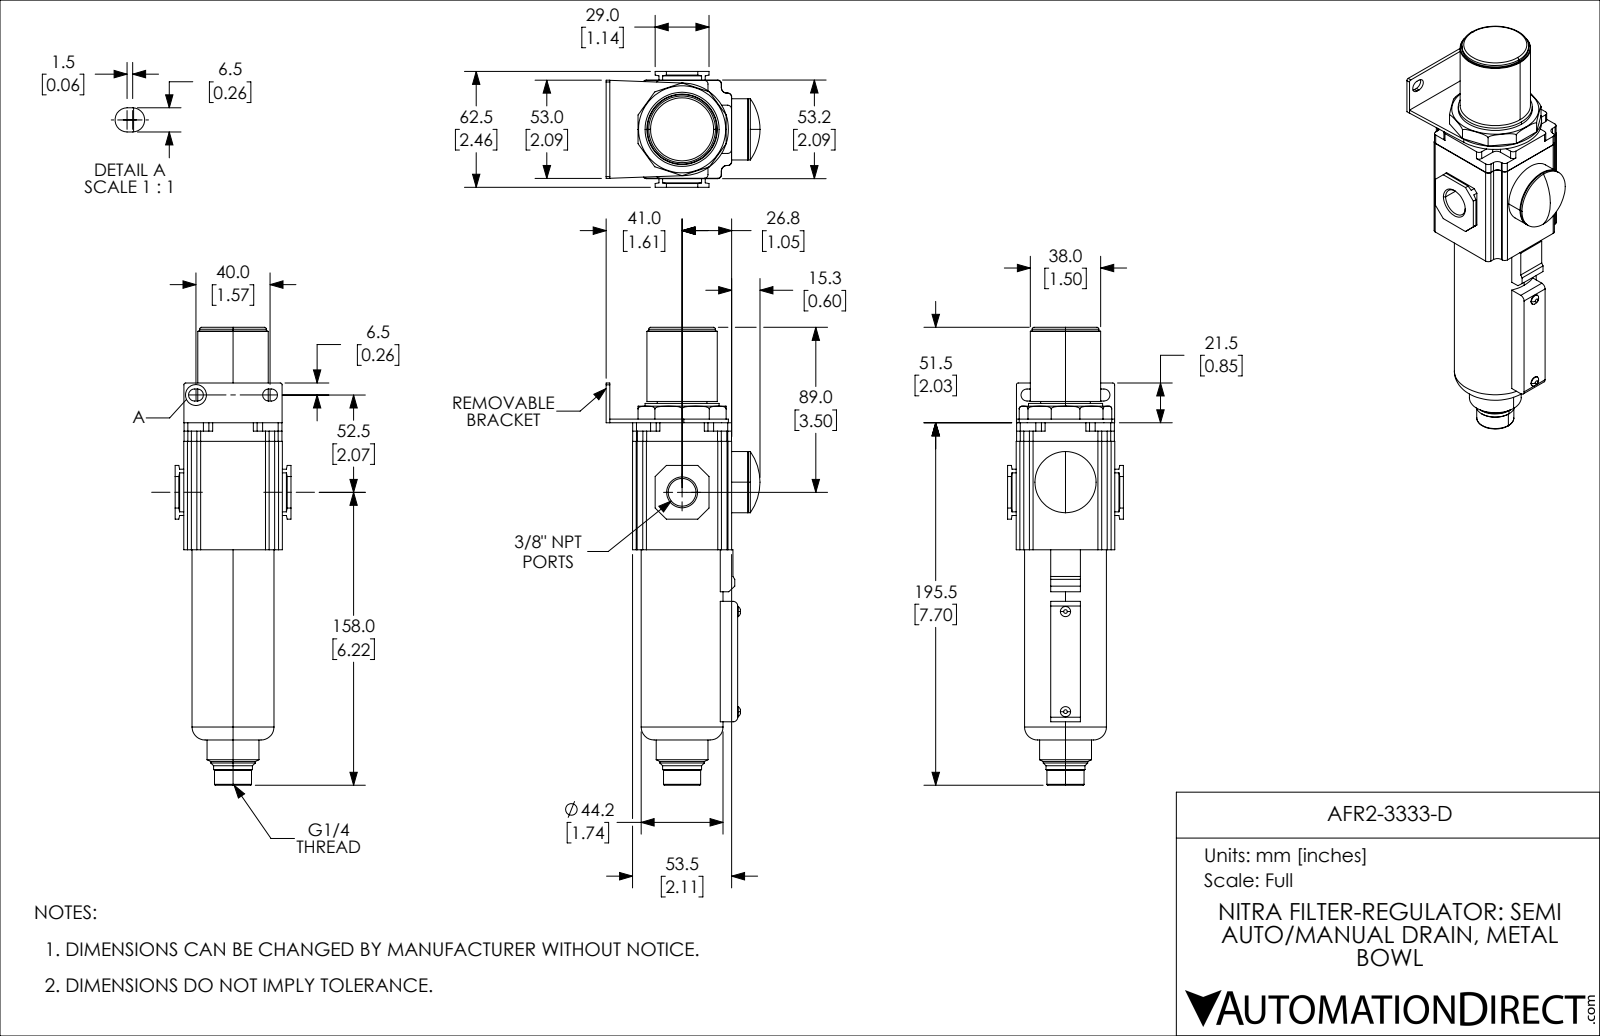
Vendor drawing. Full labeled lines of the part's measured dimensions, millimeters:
Part name (STEP PRODUCT): AFR2-3333-D
STEP written by: SolidWorks 2019 (CONFIG_CONTROL_DESIGN)
Units: millimetres
Bodies: 1 solid, 235 faces (128 planar, 77 cylindrical, 30 other)
Overall size (bounding box): 247 × 83.03 × 62.5
Volume: 438 897 mm³ · Surface area: 52 897 mm²
Round holes (diameter × count): ⌀11.45 ×1, ⌀14.95 ×1
Round bosses / shafts (diameter × count): ⌀5.5 ×2, ⌀44.2 ×1, ⌀40 ×1, ⌀38 ×1, ⌀36 ×1, ⌀33 ×1, ⌀28 ×1, ⌀26.78 ×1
Partial cylindrical surfaces — rounded edges, fillets, slot ends (radius × count): R2 ×24, R3 ×12, R3.25 ×4, R1 ×2, R2.5 ×2, R25 ×1
Main face-to-face distances: 2, 53.2, 18.6, 34.6, 16, 53.5, 39.25, 14.25, 4.65, 23.25
